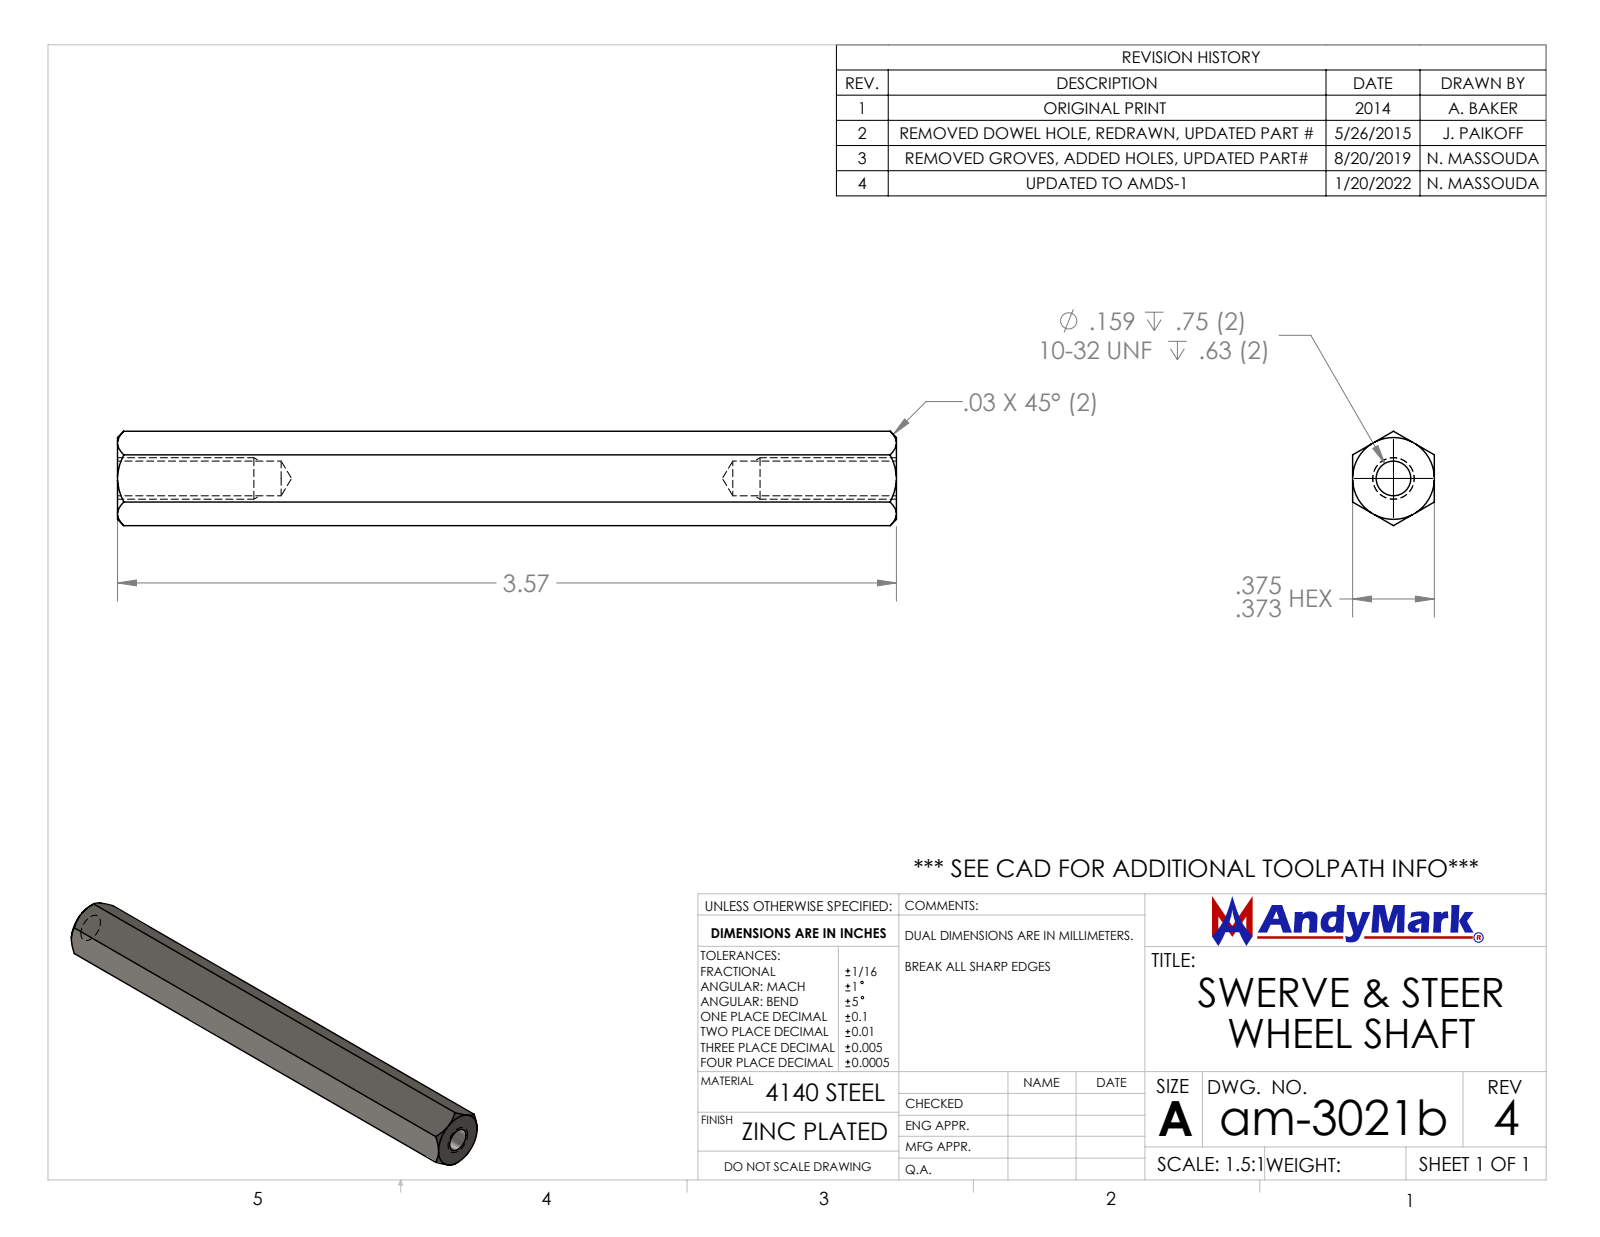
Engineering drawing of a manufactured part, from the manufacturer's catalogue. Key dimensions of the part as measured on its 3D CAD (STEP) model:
Part name (STEP PRODUCT): am-3021b 375 Hex Output Shaft Rev 4
STEP written by: SolidWorks 2021 (CONFIG_CONTROL_DESIGN)
Units: inches
Bodies: 1 solid, 28 faces (8 planar, 4 cylindrical, 16 other)
Overall size (bounding box): 3.57 × 0.432 × 0.374
Volume: 0.403 in³ · Surface area: 5.614 in²
Round holes (diameter × count): ⌀0.159 ×1
Main face-to-face distances: 0.375, 3.57
